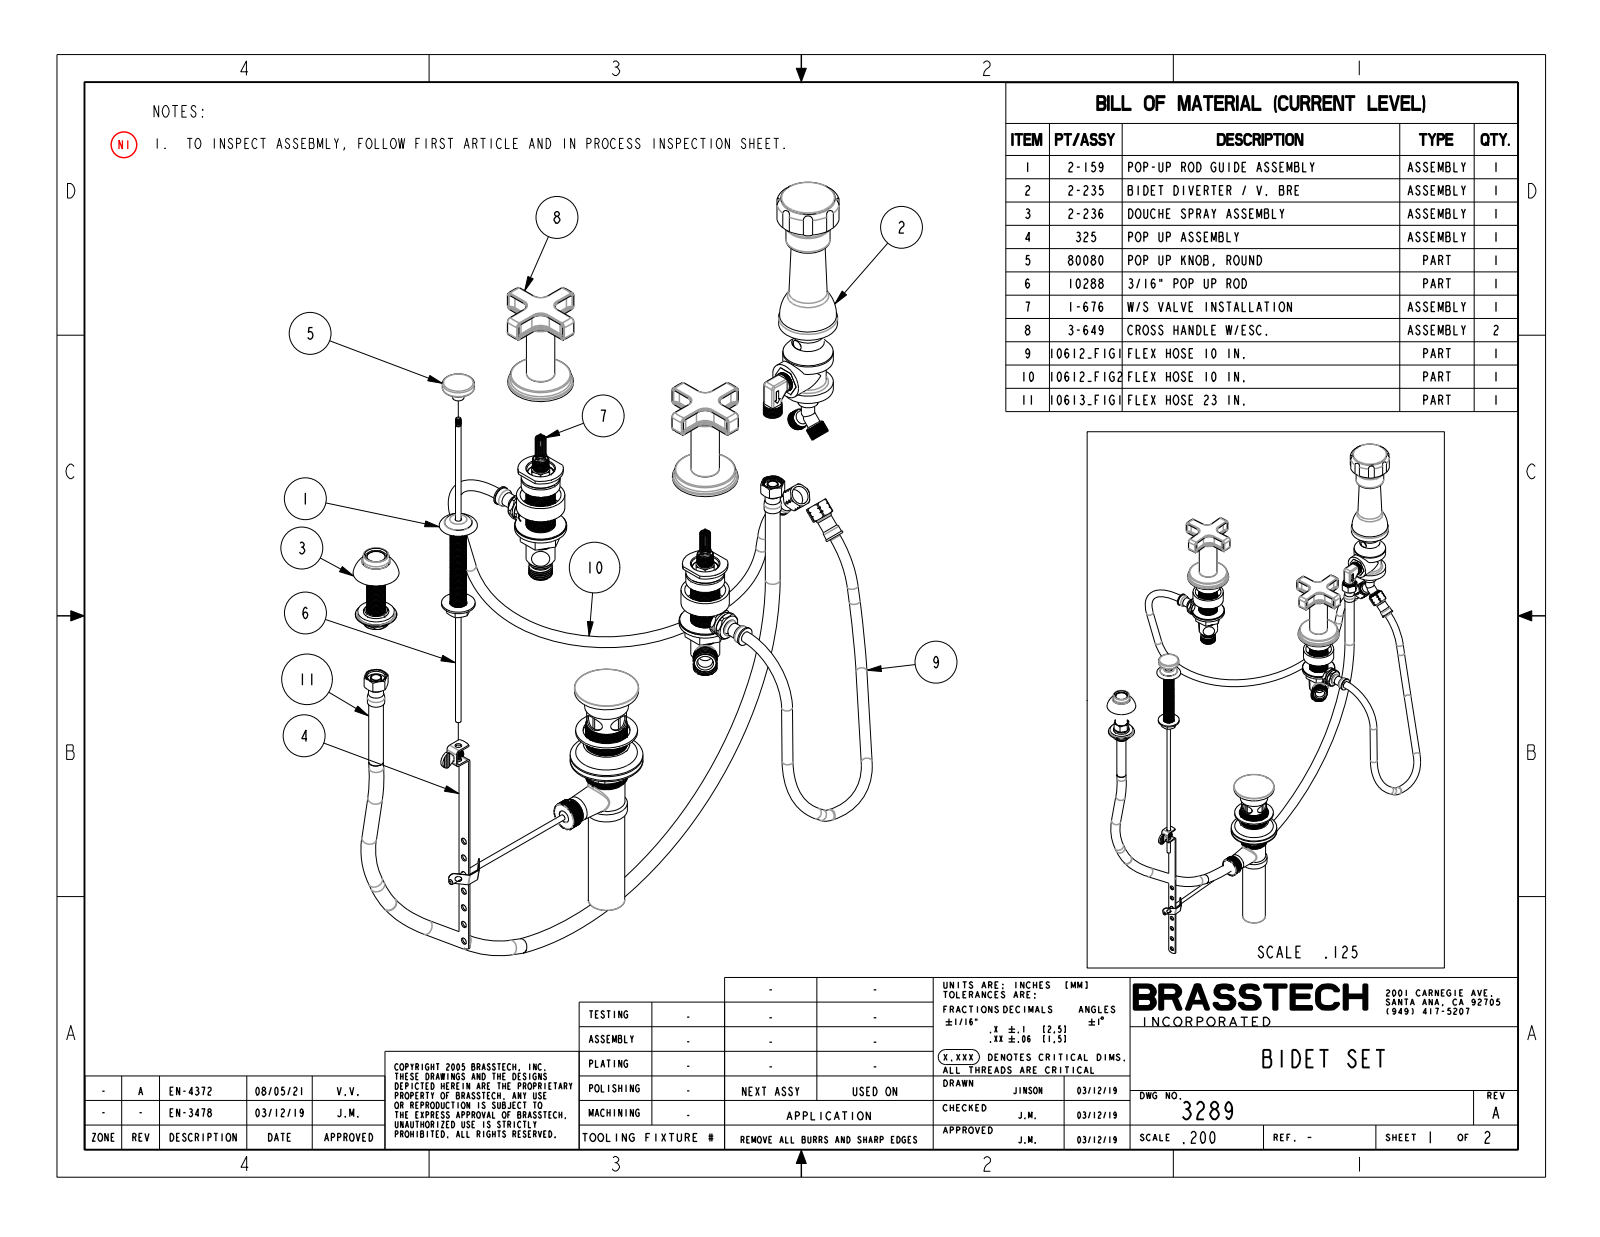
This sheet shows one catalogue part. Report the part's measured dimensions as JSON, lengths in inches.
{"part_name": "10078; 2-159_ASM; 91093; 10600 (+8 more)", "step_written_by": "CREO PARAMETRIC BY PTC INC, 2018400 (CONFIG_CONTROL_DESIGN)", "units": "inches", "bodies": {"solids": 31, "faces": 2765, "planar": 612, "cylindrical": 1247, "other": 906}, "overall_size": [22.855, 10.8, 5.373], "volume_in3": 11.75, "surface_area_in2": 291.9, "round_holes": [[0.6, 3], [0.11, 2], [0.168, 2], [0.275, 2], [0.358, 2], [0.36, 2], [0.375, 2], [0.383, 2], [0.397, 2], [0.4, 2], [0.516, 2], [0.76, 2]], "round_bosses_or_shafts": [[2.25, 2], [2.09, 2], [1.812, 2], [0.975, 2], [0.85, 2], [0.73, 2], [0.51, 2], [0.506, 2]], "partial_cylinders_radius": [[0.03, 68], [0.05, 30], [0.111, 30], [0.184, 30], [0.25, 16], [0.01, 12], [0.042, 12], [0.21, 8]], "face_to_face_distances": [2.901, 0.1, 2.201, 0.7, 2.301, 0.3, 0.35, 3.001, 0.25, 2.551], "hole_center_spacings": [8.944, 9.849, 12.649, 4, 8, 17, 21]}
